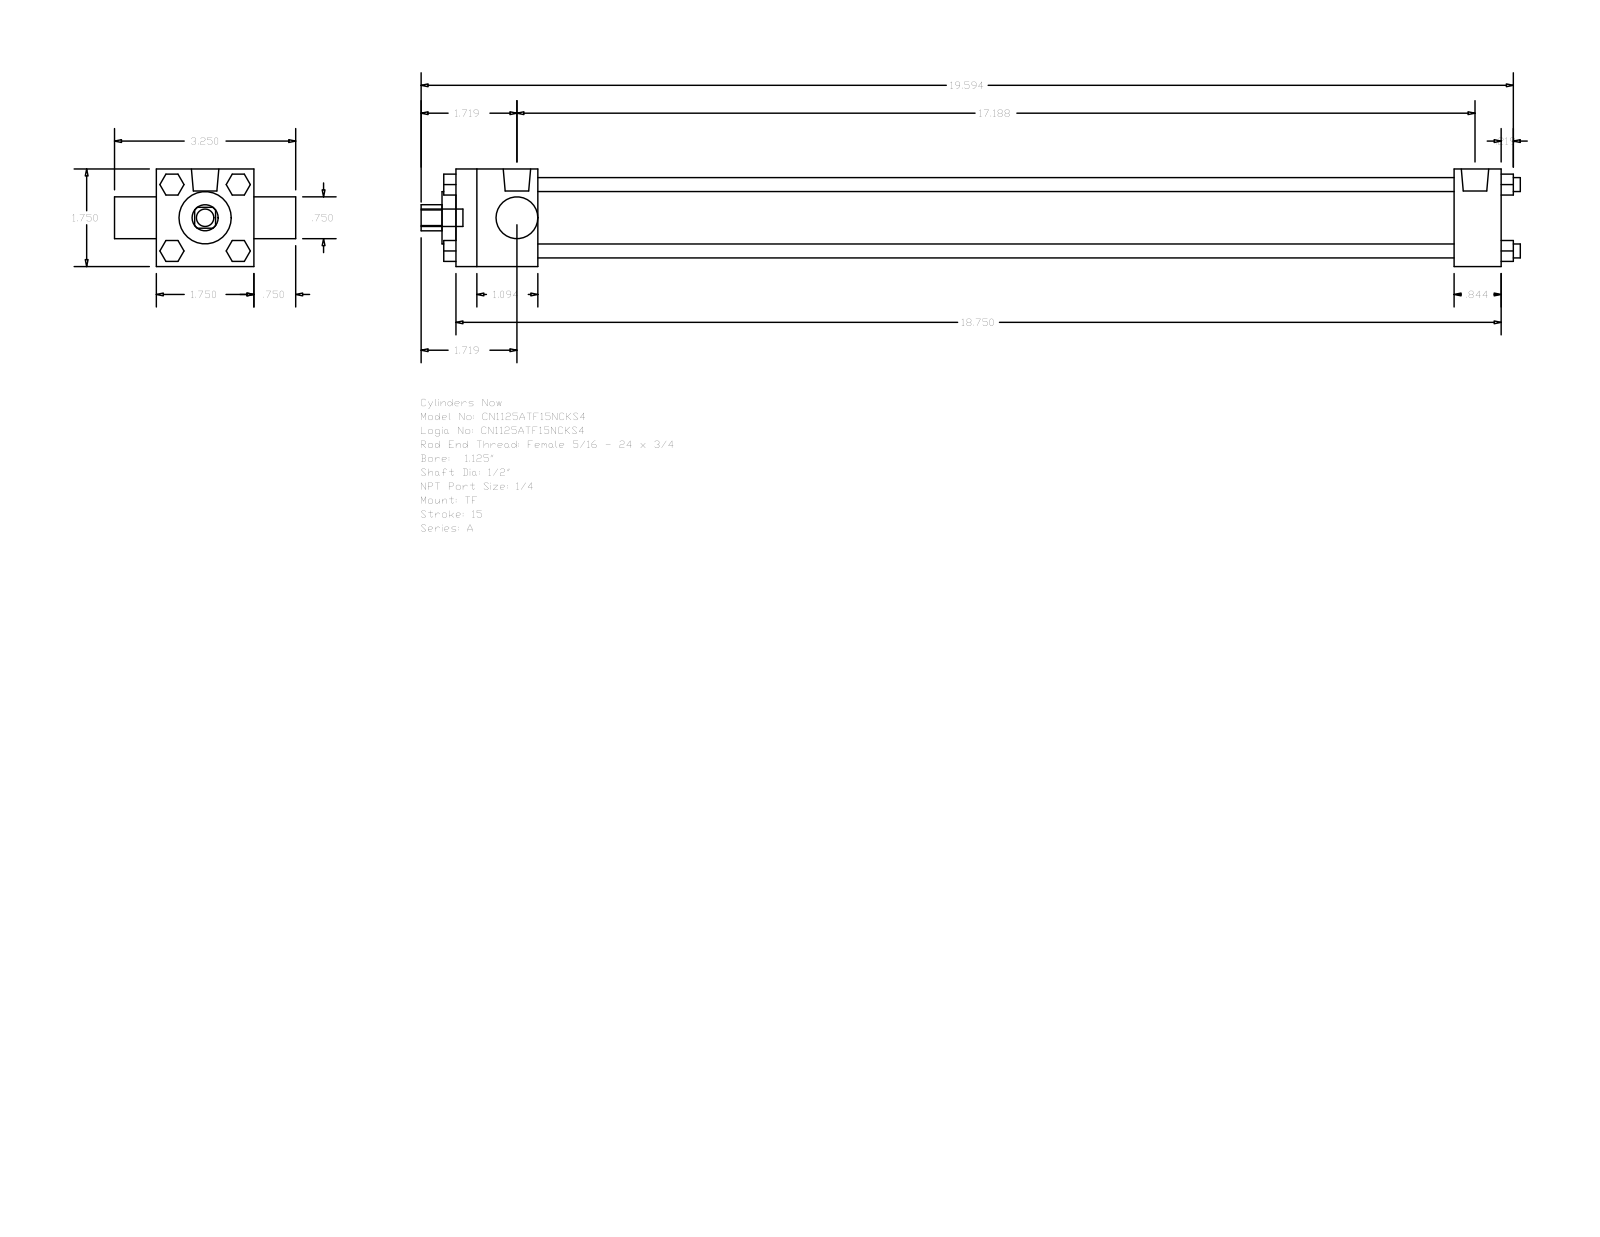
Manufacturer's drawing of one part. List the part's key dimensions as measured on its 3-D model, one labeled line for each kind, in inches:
Part name (STEP PRODUCT): A_TF__0112_0.5
STEP written by: GSSL Pune (CONFIG_CONTROL_DESIGN)
Units: inches
Bodies: 0 solids, 120 faces (92 planar, 28 cylindrical, 0 other)
Overall size (bounding box): 19.719 × 3.25 × 1.75
Round holes (diameter × count): ⌀0.5 ×1, ⌀0.75 ×1, ⌀0.937 ×1, ⌀1.255 ×1
Round bosses / shafts (diameter × count): ⌀0.25 ×4, ⌀0.219 ×3, ⌀0.492 ×2, ⌀0.313 ×1
Partial cylindrical surfaces — rounded edges, fillets, slot ends (radius × count): R0.234 ×1
Main face-to-face distances: 1.75, 18.75, 17.906, 0.844, 1.469, 16.437, 17.281, 0.75, 2.5, 0.375
